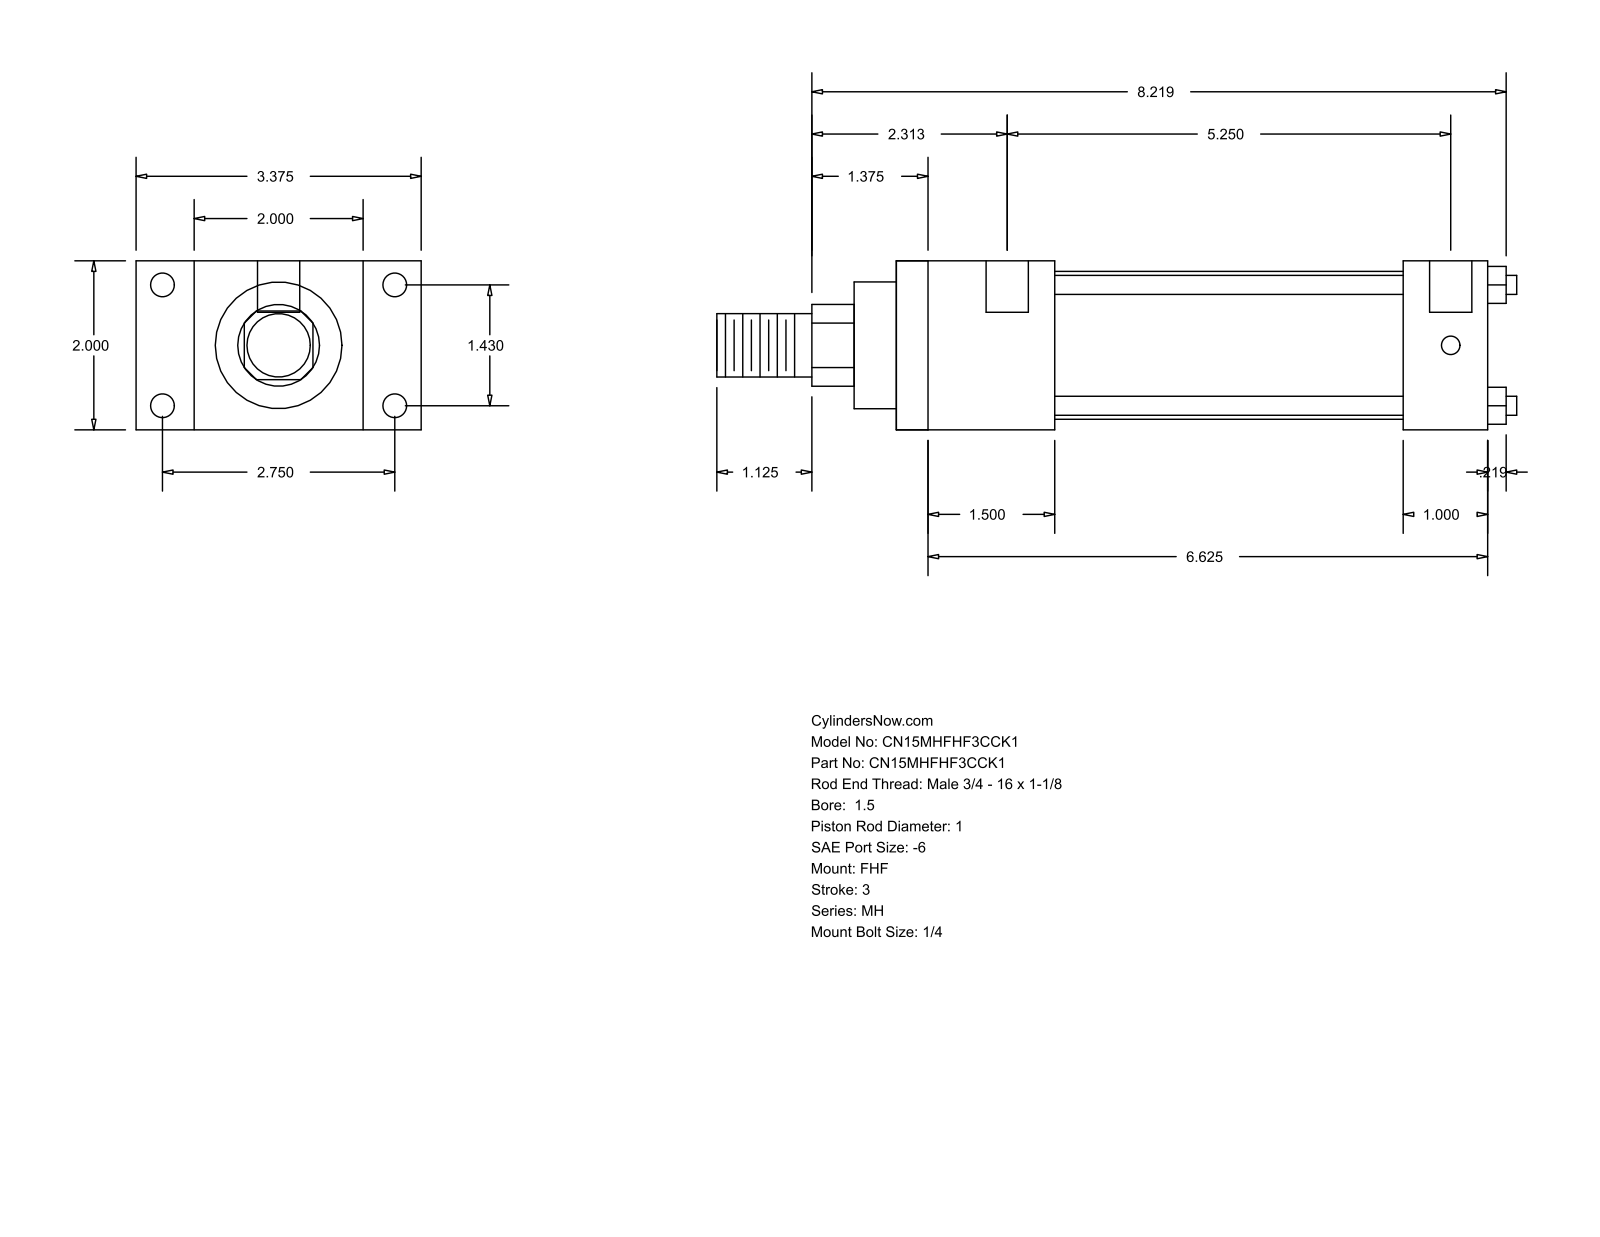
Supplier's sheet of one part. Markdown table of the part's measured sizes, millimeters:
| quantity | value |
| --- | --- |
| part name | MH_FHF__0150_1 |
| STEP written by | GSSL Pune (CONFIG_CONTROL_DESIGN) |
| units | millimeters |
| bodies | 0 solids, 88 faces (60 planar, 28 cylindrical, 0 other) |
| overall size | 240.51 × 85.72 × 50.8 |
| round holes (diameter × count) | 5.56 × 4, 7.14 × 4, 12.7 × 2 |
| round bosses / shafts (diameter × count) | 5.71 × 4, 44.45 × 1, 38.1 × 1, 25.4 × 1, 19.05 × 1 |
| partial cylindrical surfaces (radius × count) | 12.29 × 1 |
| main face-to-face distances | 50.8, 17.46, 68.26, 47.63, 85.72, 177.8, 130.17, 25.4, 152.4, 104.77 |
| hole center spacings | 36.32, 69.84, 78.72, 136.53, 3.18, 133.35 |
